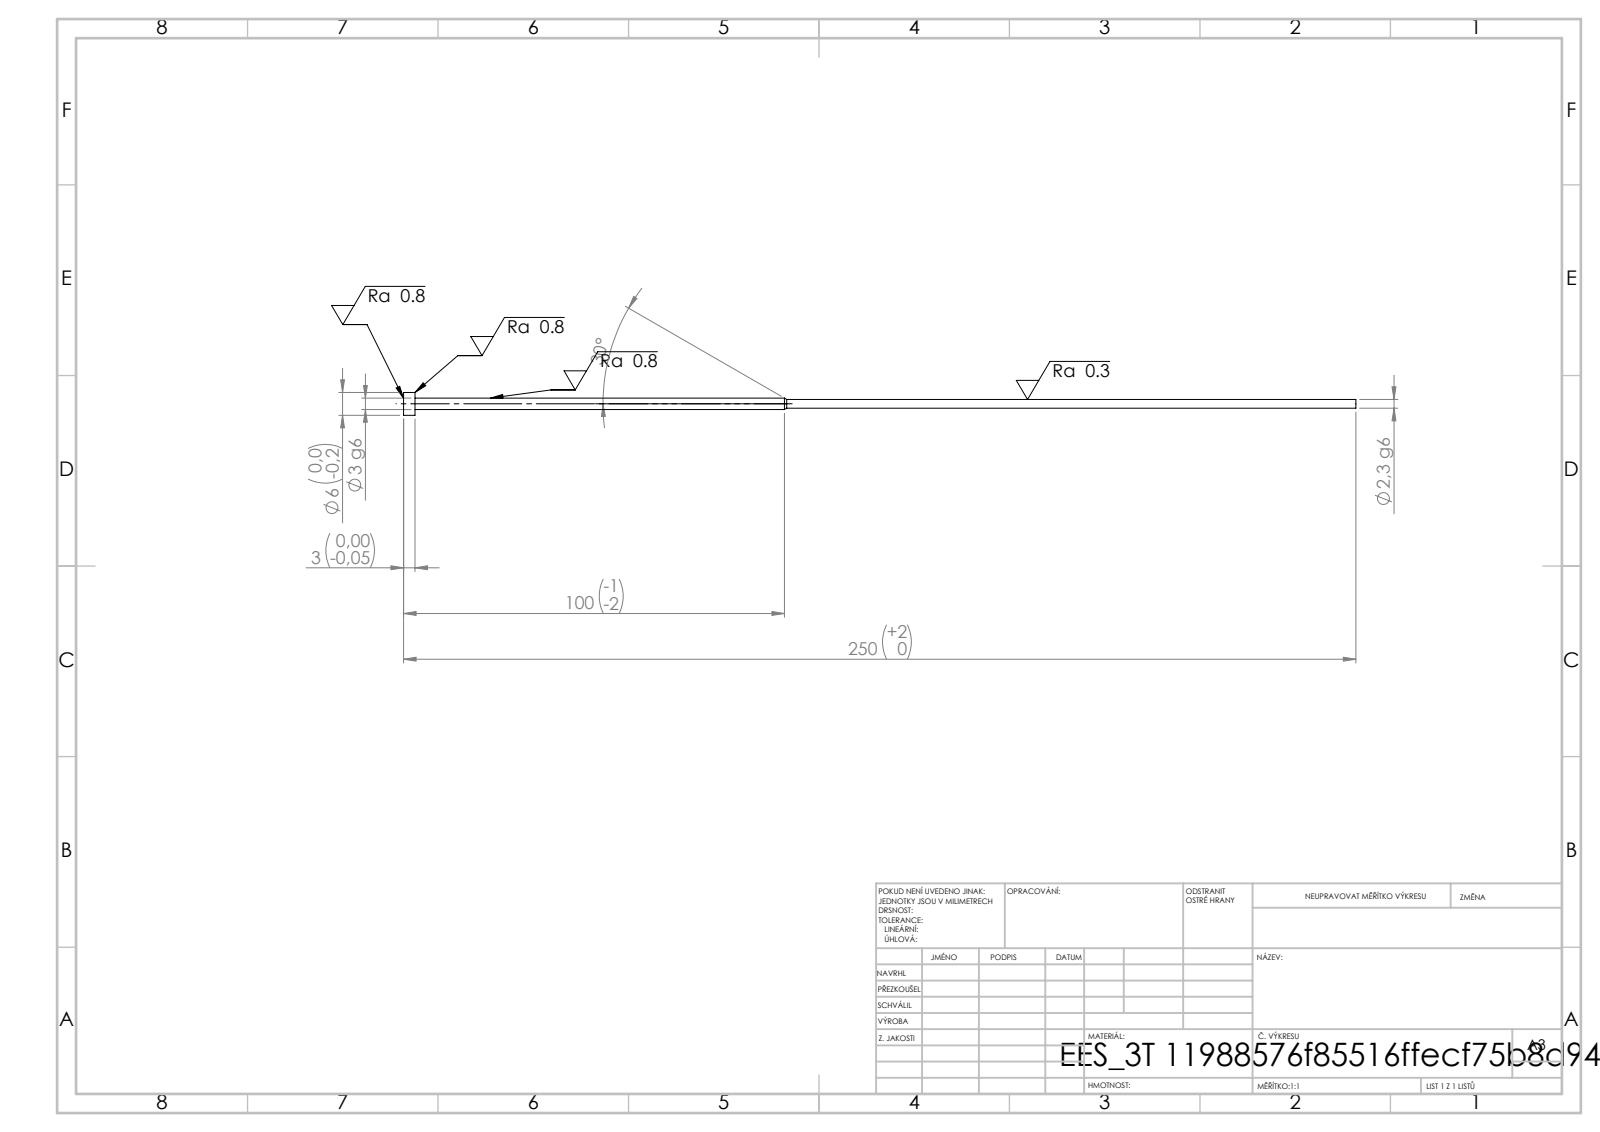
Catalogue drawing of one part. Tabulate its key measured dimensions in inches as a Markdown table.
| quantity | value |
| --- | --- |
| STEP written by | SolidWorks 2019 (CONFIG_CONTROL_DESIGN) |
| units | inches |
| bodies | 1 solid, 11 faces (3 planar, 6 cylindrical, 2 other) |
| overall size | 9.843 × 0.236 × 0.236 |
| volume | 0.085 in³ |
| surface area | 3.271 in² |
| round bosses / shafts (diameter × count) | 0.236 × 1, 0.118 × 1, 0.091 × 1 |
| main face-to-face distances | 0.118, 9.724, 9.843 |
